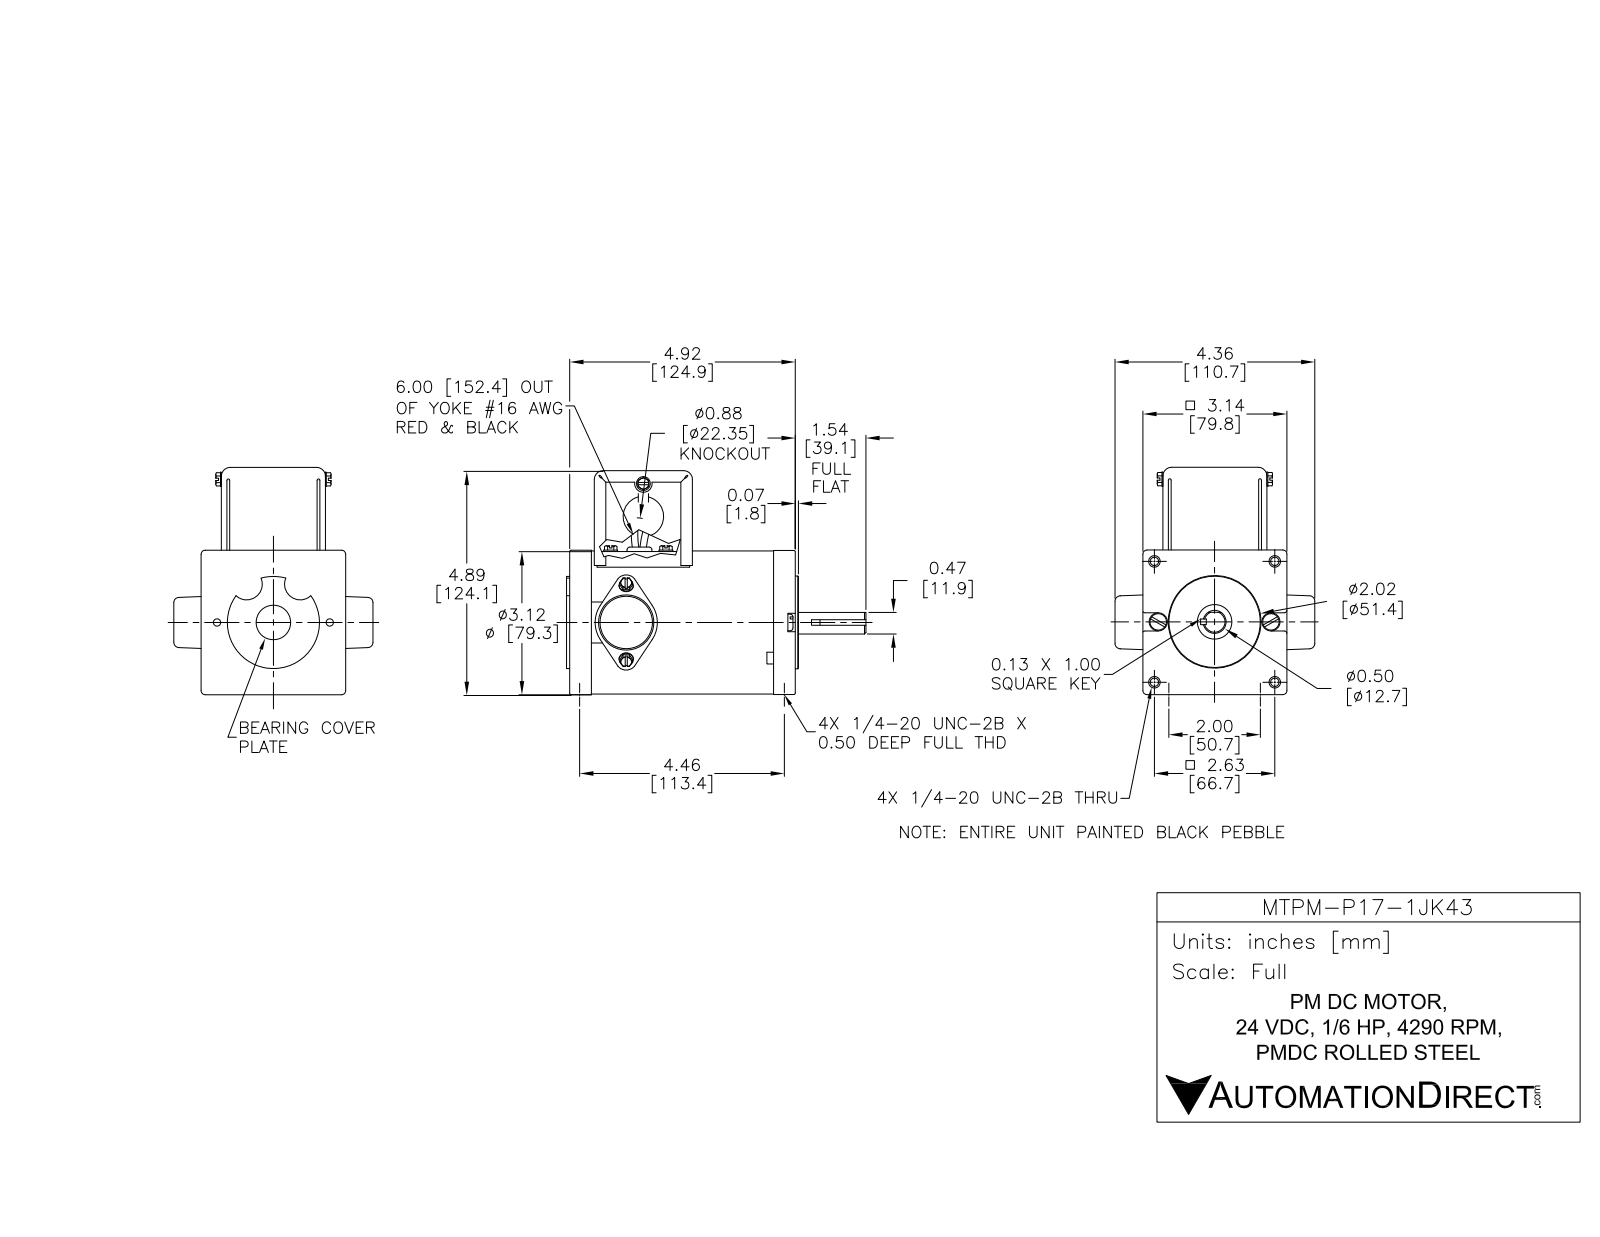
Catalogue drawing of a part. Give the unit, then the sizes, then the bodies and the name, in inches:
Units: inches
Overall size (bounding box): 6.52 × 4.944 × 4.39
Round holes (diameter × count): ⌀0.125 ×4, ⌀0.198 ×2, ⌀0.25 ×1, ⌀0.3 ×1, ⌀0.375 ×1, ⌀0.5 ×1, ⌀1.225 ×1, ⌀2.02 ×1, ⌀3 ×1, ⌀3.125 ×1
Round bosses / shafts (diameter × count): ⌀0.3 ×4, ⌀0.125 ×2, ⌀0.1 ×2, ⌀0.625 ×1
Partial cylindrical surfaces — rounded edges, fillets, slot ends (radius × count): R0.191 ×4, R0.234 ×4, R0.159 ×2, R0.341 ×2, R0.151 ×1, R0.613 ×1, R0.667 ×1, R0.678 ×1
Main face-to-face distances: 0.031, 0.25, 4.665, 0.063, 2.135, 4.415, 2.047, 0.094, 4.915, 2.198
Hole centre spacings: 1.318, 1.859, 2.63, 2.865, 1.23, 3.719, 2.46, 3.083
Volume: 12.13 in³ · Surface area: 231.8 in²
Bodies: 28 solids, 410 faces (271 planar, 114 cylindrical, 25 other)
Part name (STEP PRODUCT): MTPM-P17-1JK43
STEP written by: SolidWorks 2017 (AUTOMOTIVE_DESIGN)
